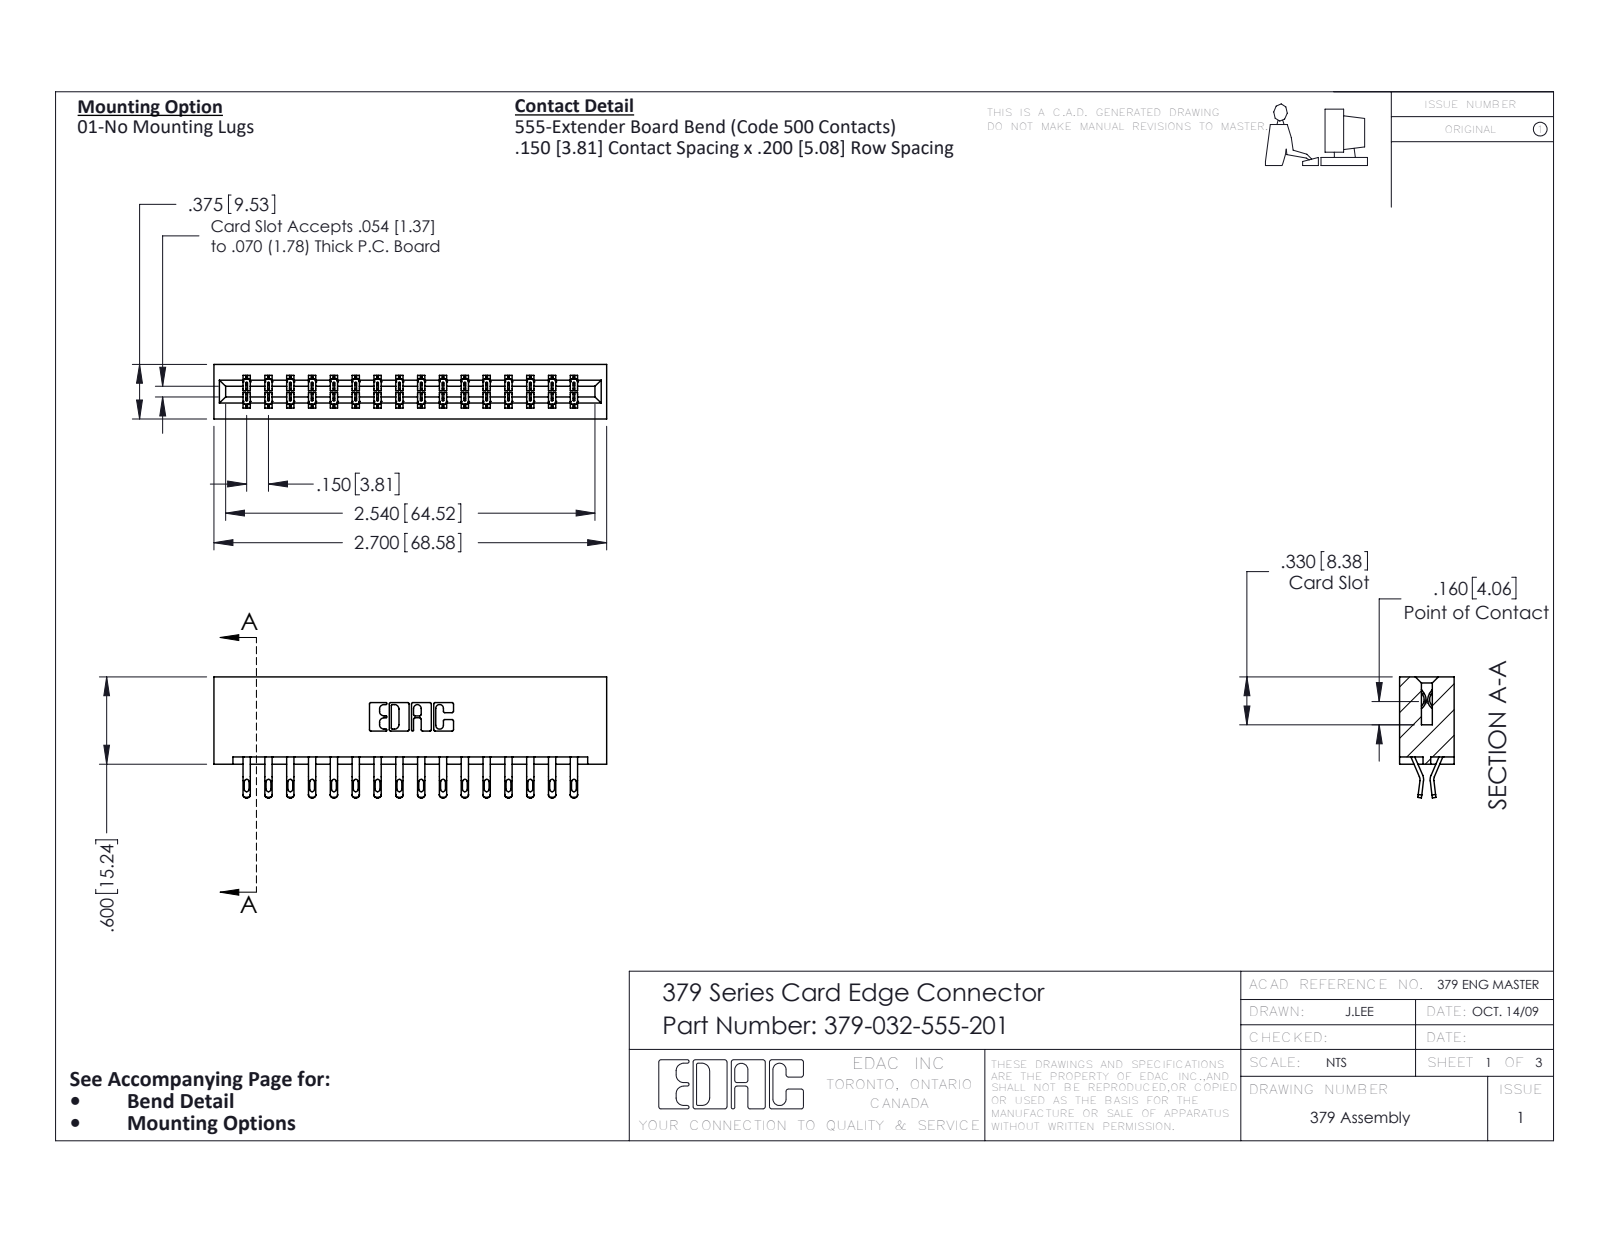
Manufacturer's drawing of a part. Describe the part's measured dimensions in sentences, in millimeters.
The part is named "379 Part_Lugless; 379-032-555-201; 345-292-001_555 Tail". Its 3-D file was written by "SolidWorks 2020 (CONFIG_CONTROL_DESIGN)". It is 33 solids with 1962 faces: 1154 planar, 808 cylindrical and 0 other. Overall it measures 68.6 by 21.1 by 9.5 millimeters. Its volume is 7 820 cubic millimeters and its surface area 8 929 square millimeters. Partial cylindrical surfaces (rounded edges, fillets, slot ends): 64 of radius 0.4, 64 of radius 0.5, 49 of radius 0.2, 22 of radius 0.3, 6 of radius 0.2, 6 of radius 0.8, 3 of radius 0.7, 2 of radius 0.3. The main face-to-face distances are 7.6, 1.9, 3.8, 9.5, 5.1, 2.5, 15.2, 11.4, 14, 1.3.
